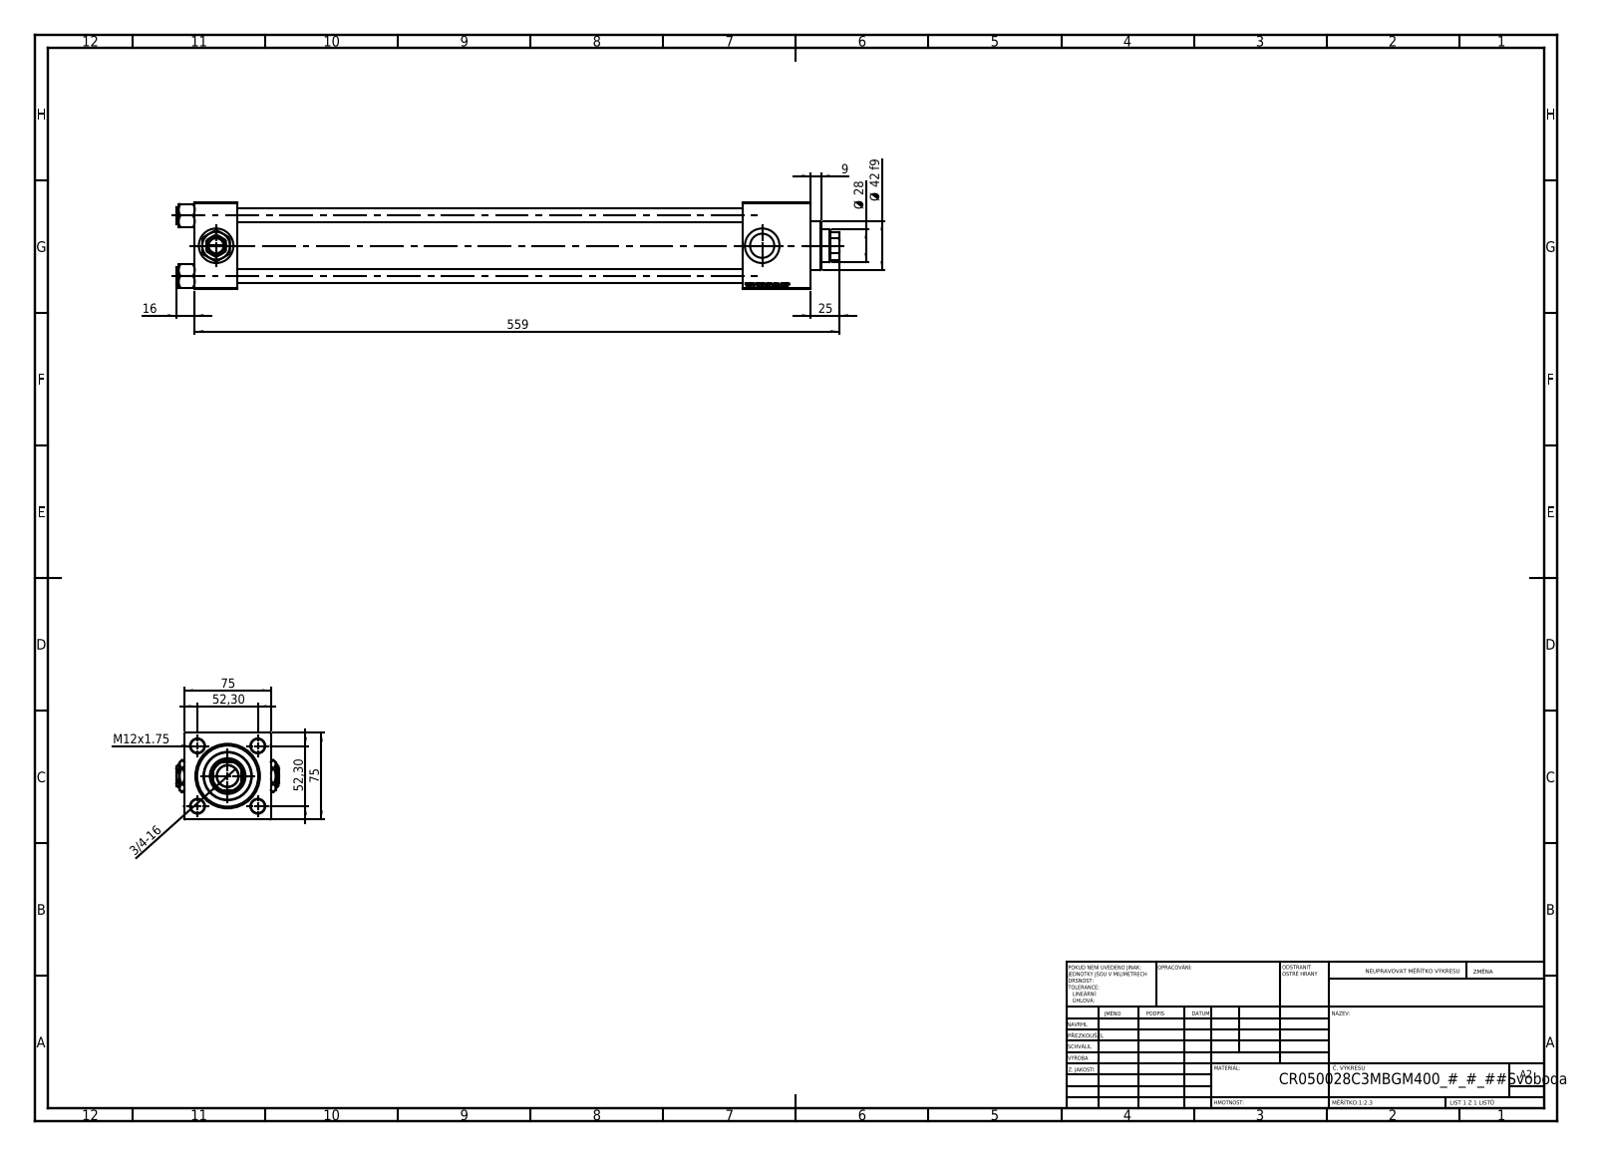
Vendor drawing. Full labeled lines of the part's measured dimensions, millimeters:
Part name (STEP PRODUCT): V215CR_C_Body; V215CR_VCP_C; V215_VC_A; Zatka_pro_OIL_PORT (+2 more)
STEP written by: SolidWorks 2019 (CONFIG_CONTROL_DESIGN)
Units: millimetres
Bodies: 13 solids, 1249 faces (573 planar, 98 cylindrical, 578 other)
Overall size (bounding box): 575 × 89 × 75
Volume: 1 260 000 mm³ · Surface area: 372 682 mm²
Round holes (diameter × count): ⌀12 ×4, ⌀7 ×2, ⌀20.96 ×2, ⌀30 ×2, ⌀18.5 ×1, ⌀28 ×1, ⌀31 ×1, ⌀41 ×1, ⌀50 ×1, ⌀53 ×1
Round bosses / shafts (diameter × count): ⌀15 ×4, ⌀56 ×1, ⌀42 ×1
Partial cylindrical surfaces — rounded edges, fillets, slot ends (radius × count): R13.5 ×1
Main face-to-face distances: 75, 37, 534, 497, 475, 438, 59, 505.3, 468.3, 30.3
Hole centre spacings: 36.98, 52.3, 73.96, 473.5
